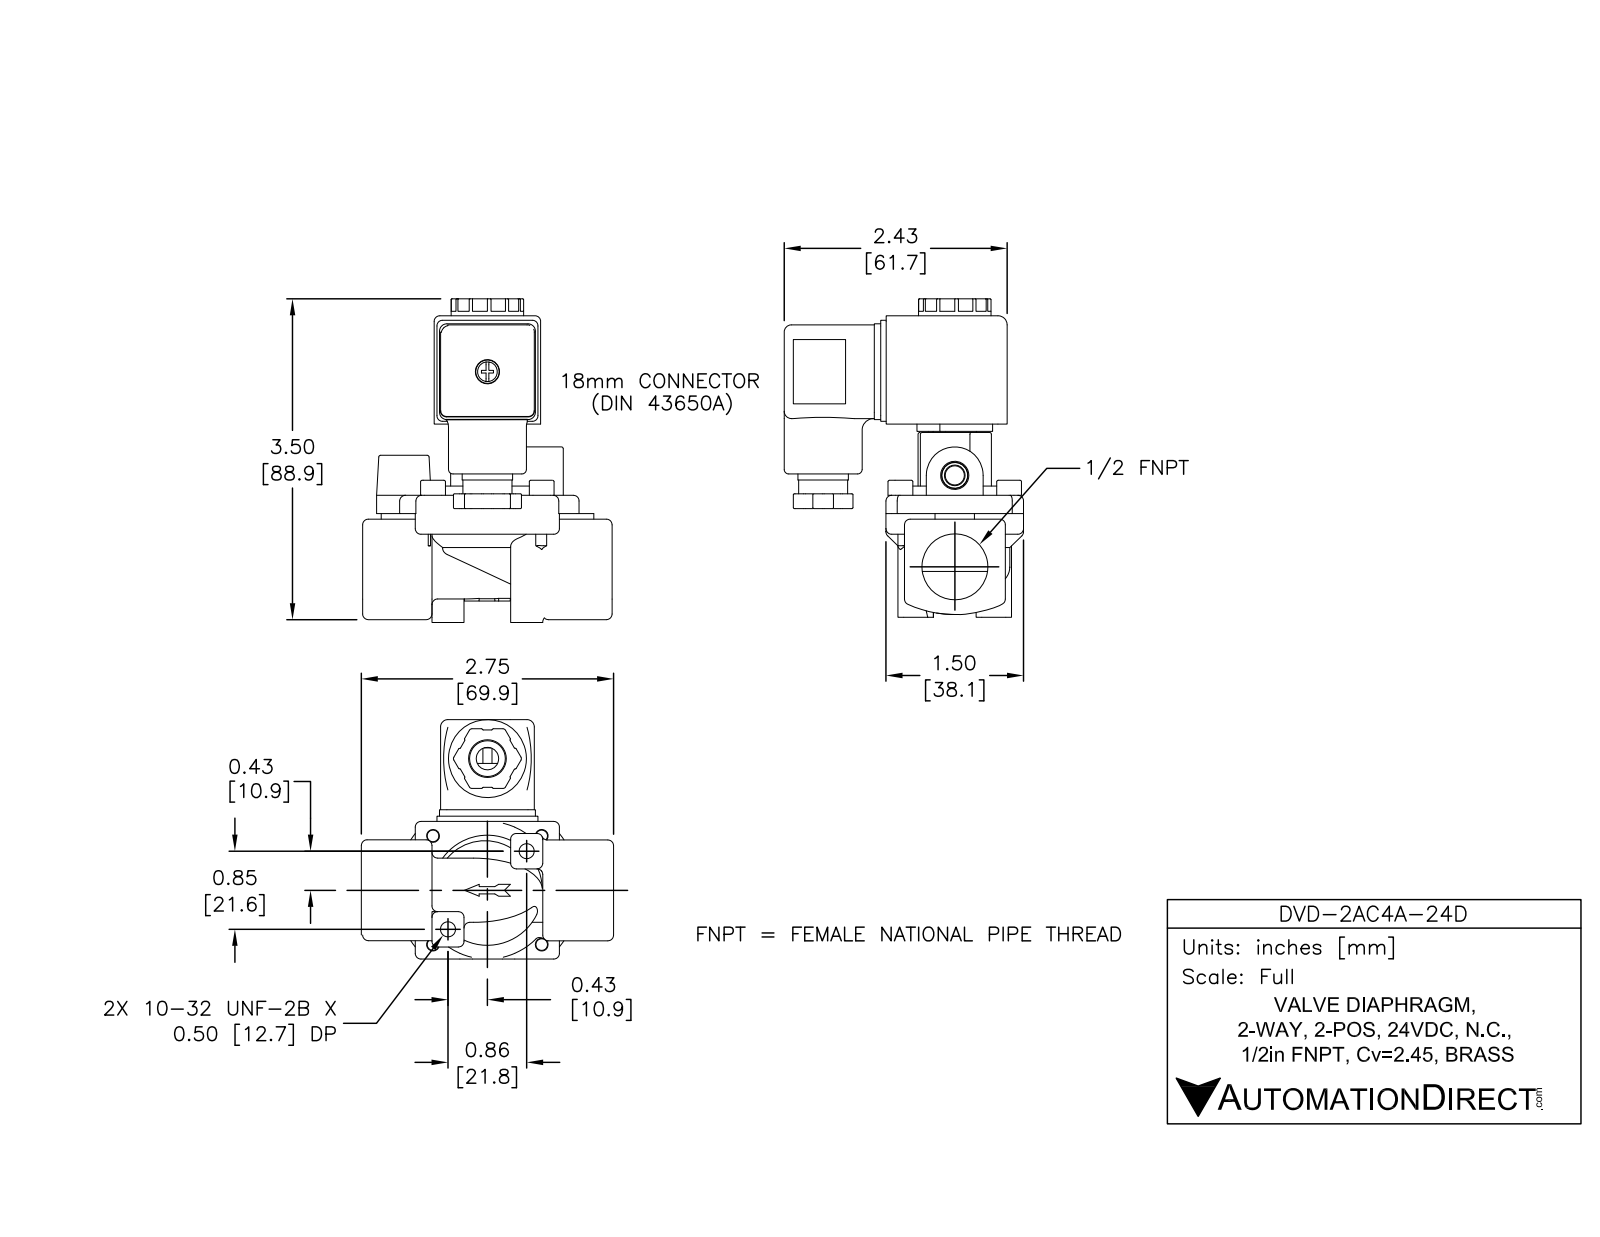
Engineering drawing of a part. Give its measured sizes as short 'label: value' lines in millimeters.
name: DVD-2AC4A-24D
written by: SolidWorks 2015 (AUTOMOTIVE_DESIGN)
unit: mm
bodies: 9 solids, 1878 faces (872 planar, 415 cylindrical, 591 other)
size: 88.2 × 69.1 × 66.3
volume: 92 240 mm³; area: 44 350 mm²
holes: 6× ⌀4.2, 4× ⌀3.5, 2× ⌀1.5, 2× ⌀2.5, 2× ⌀3.6, 2× ⌀11, 2× ⌀17.9, 1× ⌀1.6, 1× ⌀2, 1× ⌀2.3, 1× ⌀2.4, 1× ⌀2.6
bosses: 4× ⌀6.9, 4× ⌀4.5, 4× ⌀4.1, 1× ⌀34.9, 1× ⌀21.6, 1× ⌀20.1, 1× ⌀15.5, 1× ⌀15
rounds: 52× R0.3, 22× R1.6, 21× R1.6, 14× R1.6, 12× R2, 12× R4, 8× R1.3, 6× R0.8
face distances: 23.5, 5.1, 29.5, 30, 26.3, 27.9, 2, 1.5, 24.3, 33
hole spacings: 21.3, 23.5, 23.5, 30.1, 11.4, 19.8, 31.2, 5.9
